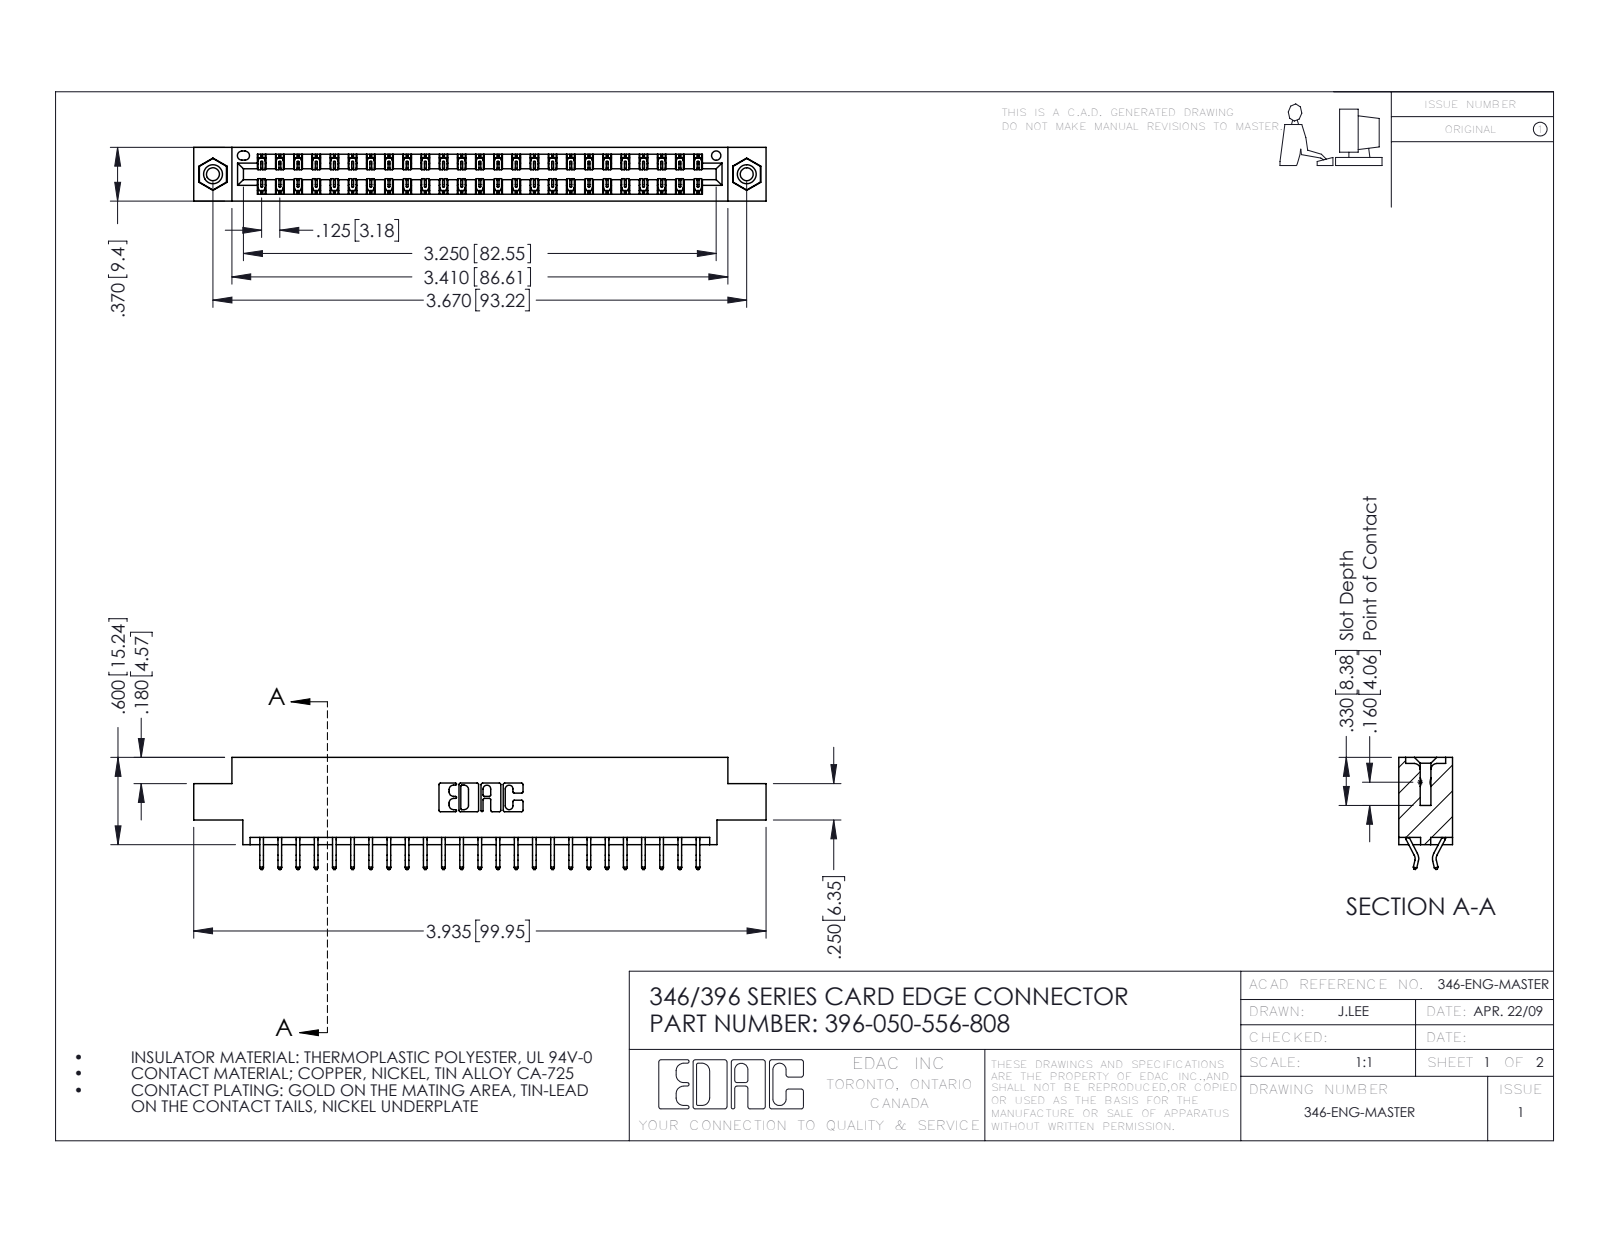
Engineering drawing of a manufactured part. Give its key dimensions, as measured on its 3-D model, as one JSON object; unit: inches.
{"part_name": "396-050-556-808; 346 Part_0.170 Offset - 0.156 Dia-TI; 345-292-001_556 Tail; 345-250-001_345-250-003-102", "step_written_by": "SolidWorks 2016 (CONFIG_CONTROL_DESIGN)", "units": "inches", "bodies": {"solids": 53, "faces": 3086, "planar": 2062, "cylindrical": 1008, "other": 16}, "overall_size": [3.935, 0.77, 0.37], "volume_in3": 0.577, "surface_area_in2": 19.96, "round_holes": [[0.089, 2], [0.125, 2], [0.156, 2], [0.064, 1]], "round_bosses_or_shafts": [[0.155, 2]], "partial_cylinders_radius": [[0.006, 75], [0.01, 22], [0.007, 6], [0.031, 6], [0.026, 3], [0.01, 2], [0.014, 2], [0.022, 2]], "face_to_face_distances": [0.048, 0.322, 0.37, 0.25, 0.025, 0.072, 0.298, 0.275, 0.222, 0.148], "hole_center_spacings": [0.246, 3.462, 3.67]}
